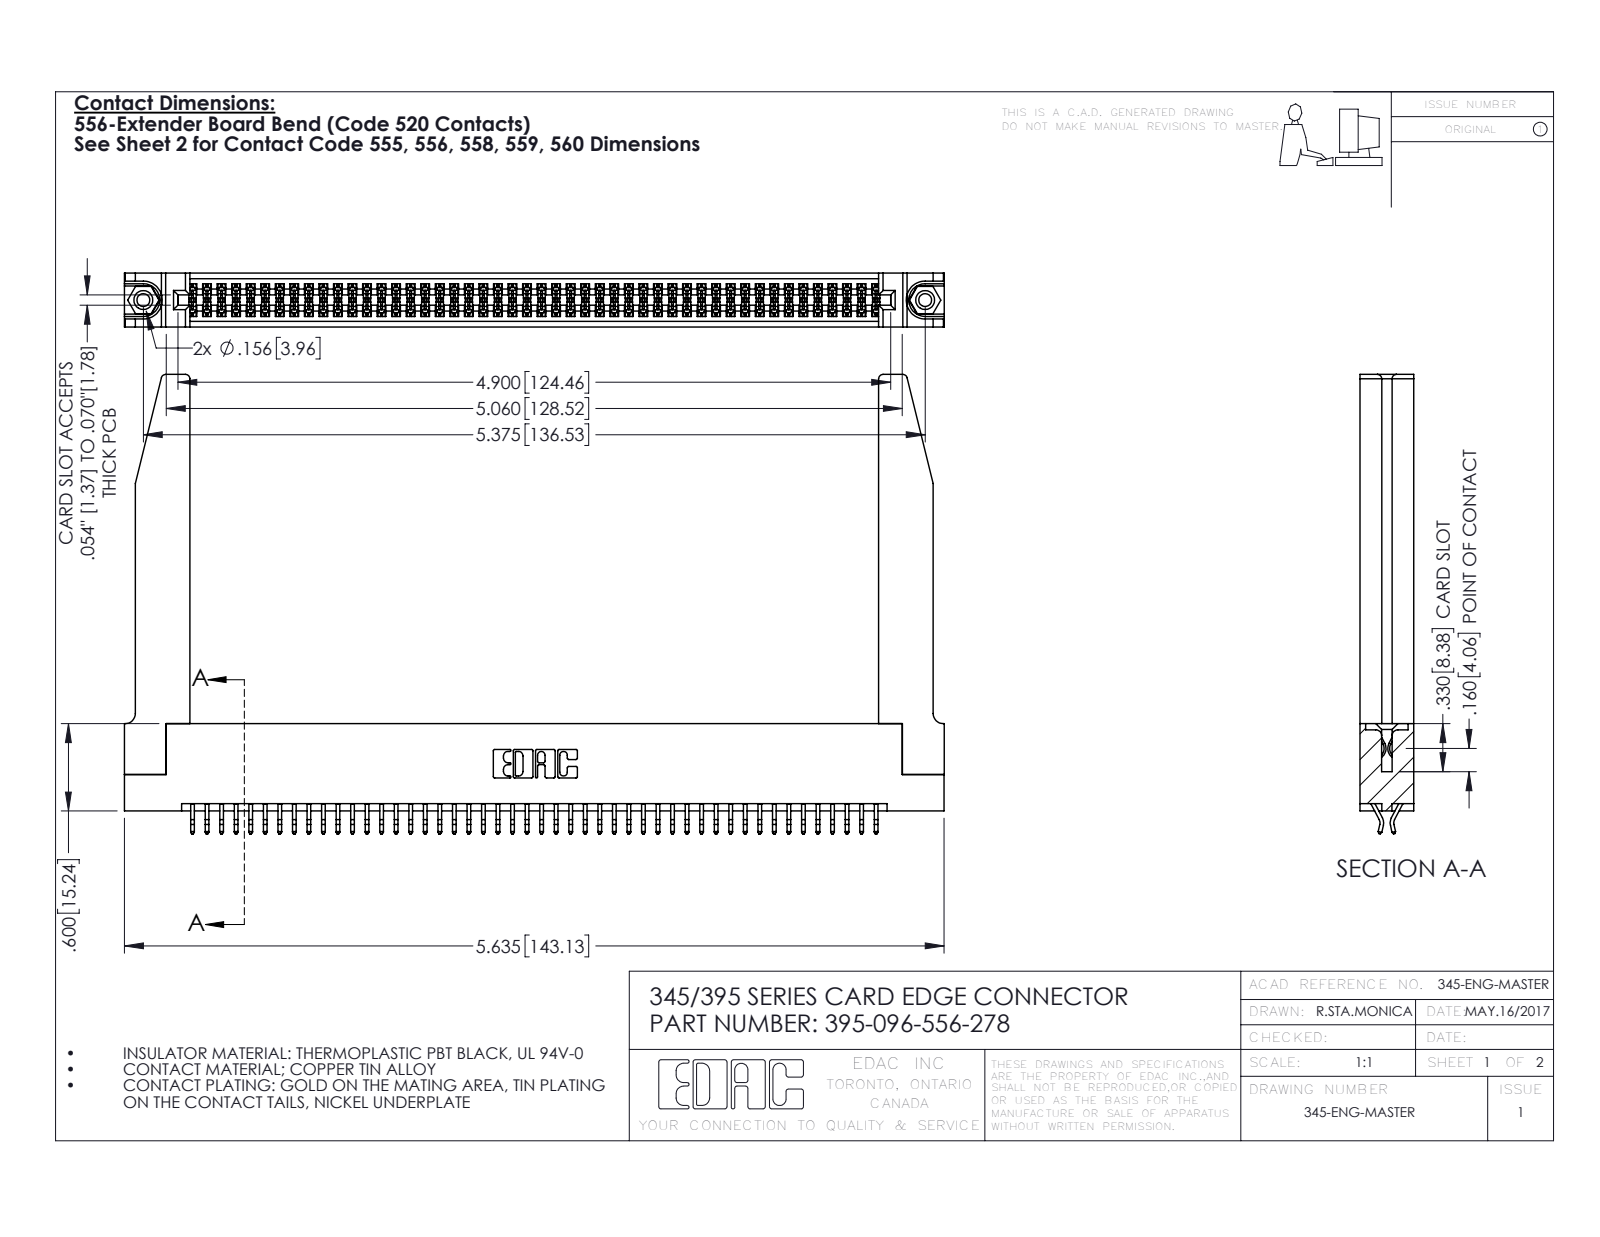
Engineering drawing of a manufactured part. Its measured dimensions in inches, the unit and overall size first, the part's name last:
Units: inches
Overall size (bounding box): 5.636 × 3.157 × 0.37
Round holes (diameter × count): ⌀0.089 ×2, ⌀0.125 ×2, ⌀0.156 ×2, ⌀0.064 ×1
Round bosses / shafts (diameter × count): ⌀0.155 ×2
Partial cylindrical surfaces — rounded edges, fillets, slot ends (radius × count): R0.006 ×144, R0.01 ×22, R0.03 ×8, R0.007 ×6, R0.031 ×6, R0.026 ×3, R0.01 ×2, R0.014 ×2
Main face-to-face distances: 0.072, 0.37, 0.298, 0.2, 0.025, 0.098, 0.272, 0.225, 0.15, 0.148
Hole centre spacings: 0.27, 5.139, 5.375
Volume: 1.326 in³ · Surface area: 42.63 in²
Bodies: 101 solids, 5736 faces (3774 planar, 1910 cylindrical, 52 other)
Part name (STEP PRODUCT): 345-292-001_556 Tail; 345-220-078_345-220-078; 345 Part_Flush Mounting Lugs - 0.156 Dia-TH; 345-250-001_345-250-001-102 (+1 more)
STEP written by: SolidWorks 2016 (CONFIG_CONTROL_DESIGN)
